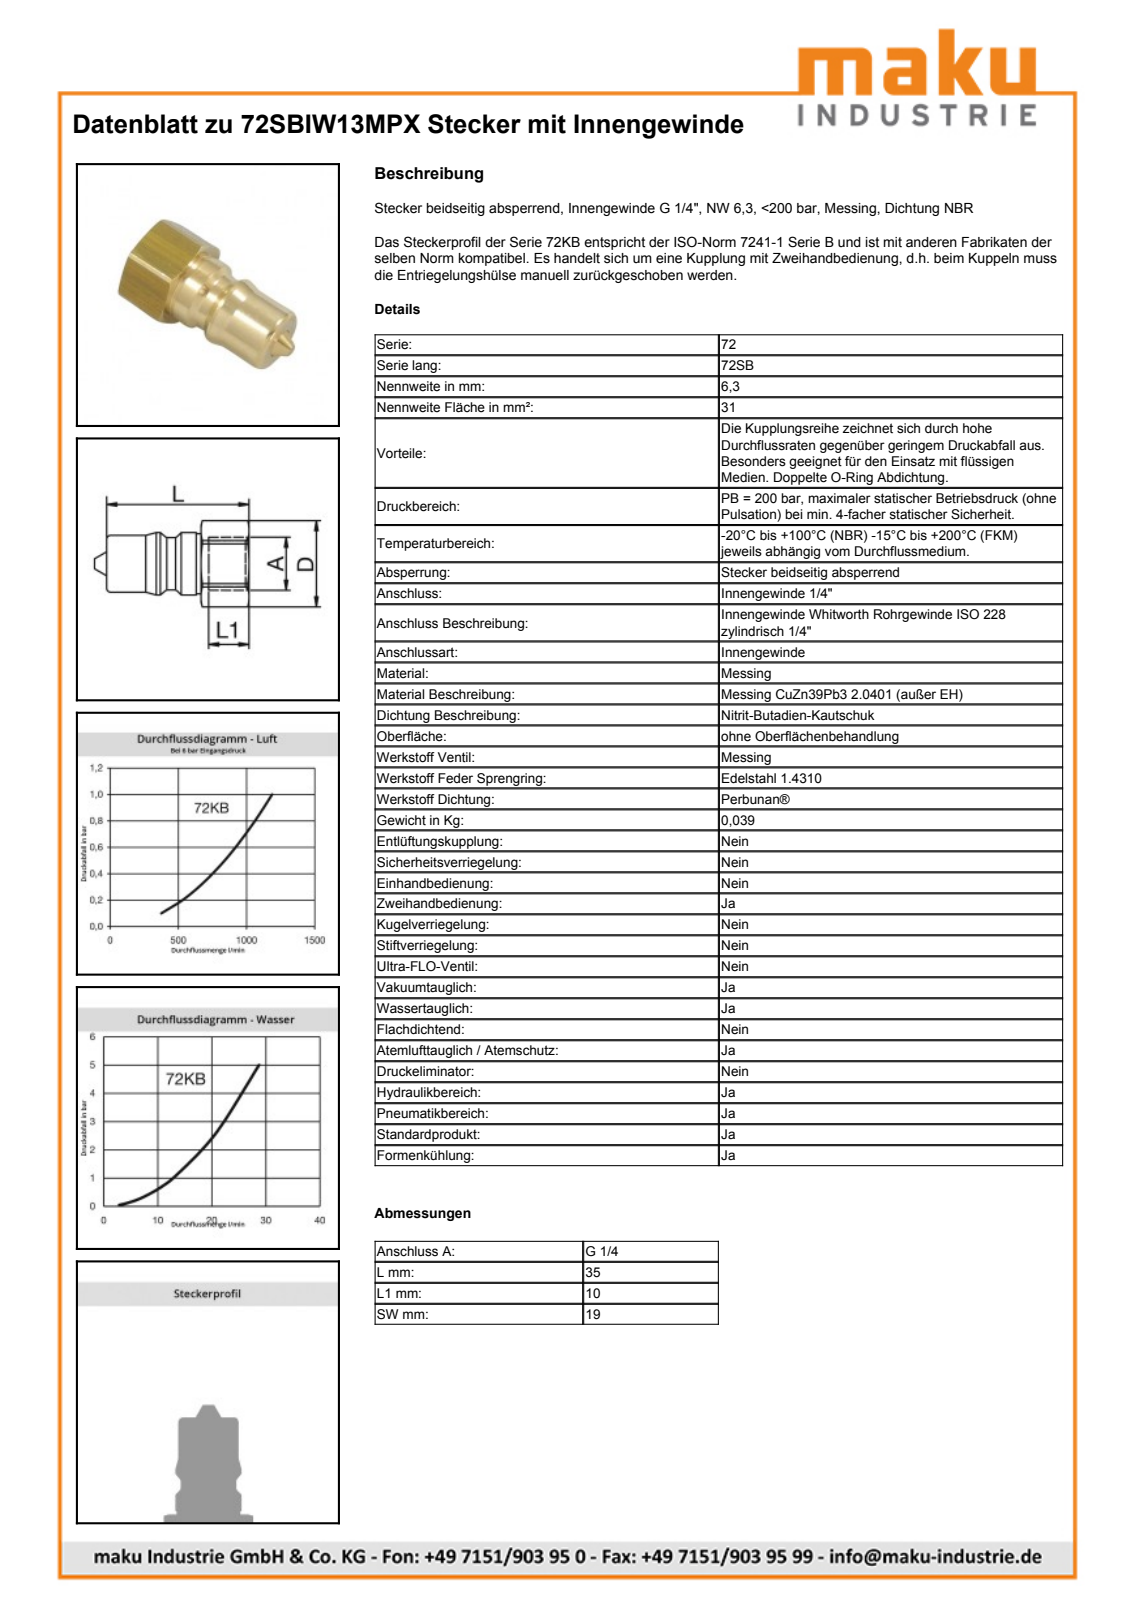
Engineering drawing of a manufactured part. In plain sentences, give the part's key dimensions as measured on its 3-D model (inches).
The part is named "D110474". Its 3-D file was written by "Autodesk Inventor 2013 (AUTOMOTIVE_DESIGN)". It is 1 solid with 46 faces: 12 planar, 12 cylindrical and 22 other. Overall it measures 1.508 by 0.843 by 0.748 inches. Its volume is 0.381 cubic inches and its surface area 4.551 square inches. Round holes: 1 of diameter 0.451. Round bosses or shafts: 1 of diameter 0.616, 1 of diameter 0.587, 1 of diameter 0.557, 1 of diameter 0.512. Partial cylindrical surfaces (rounded edges, fillets, slot ends): 1 of radius 0.421. The main face-to-face distances are 0.748, 0.512, 0.043, 0.469, 0.878, 0.921, 1.39, 0.874, 0.047, 0.516.
